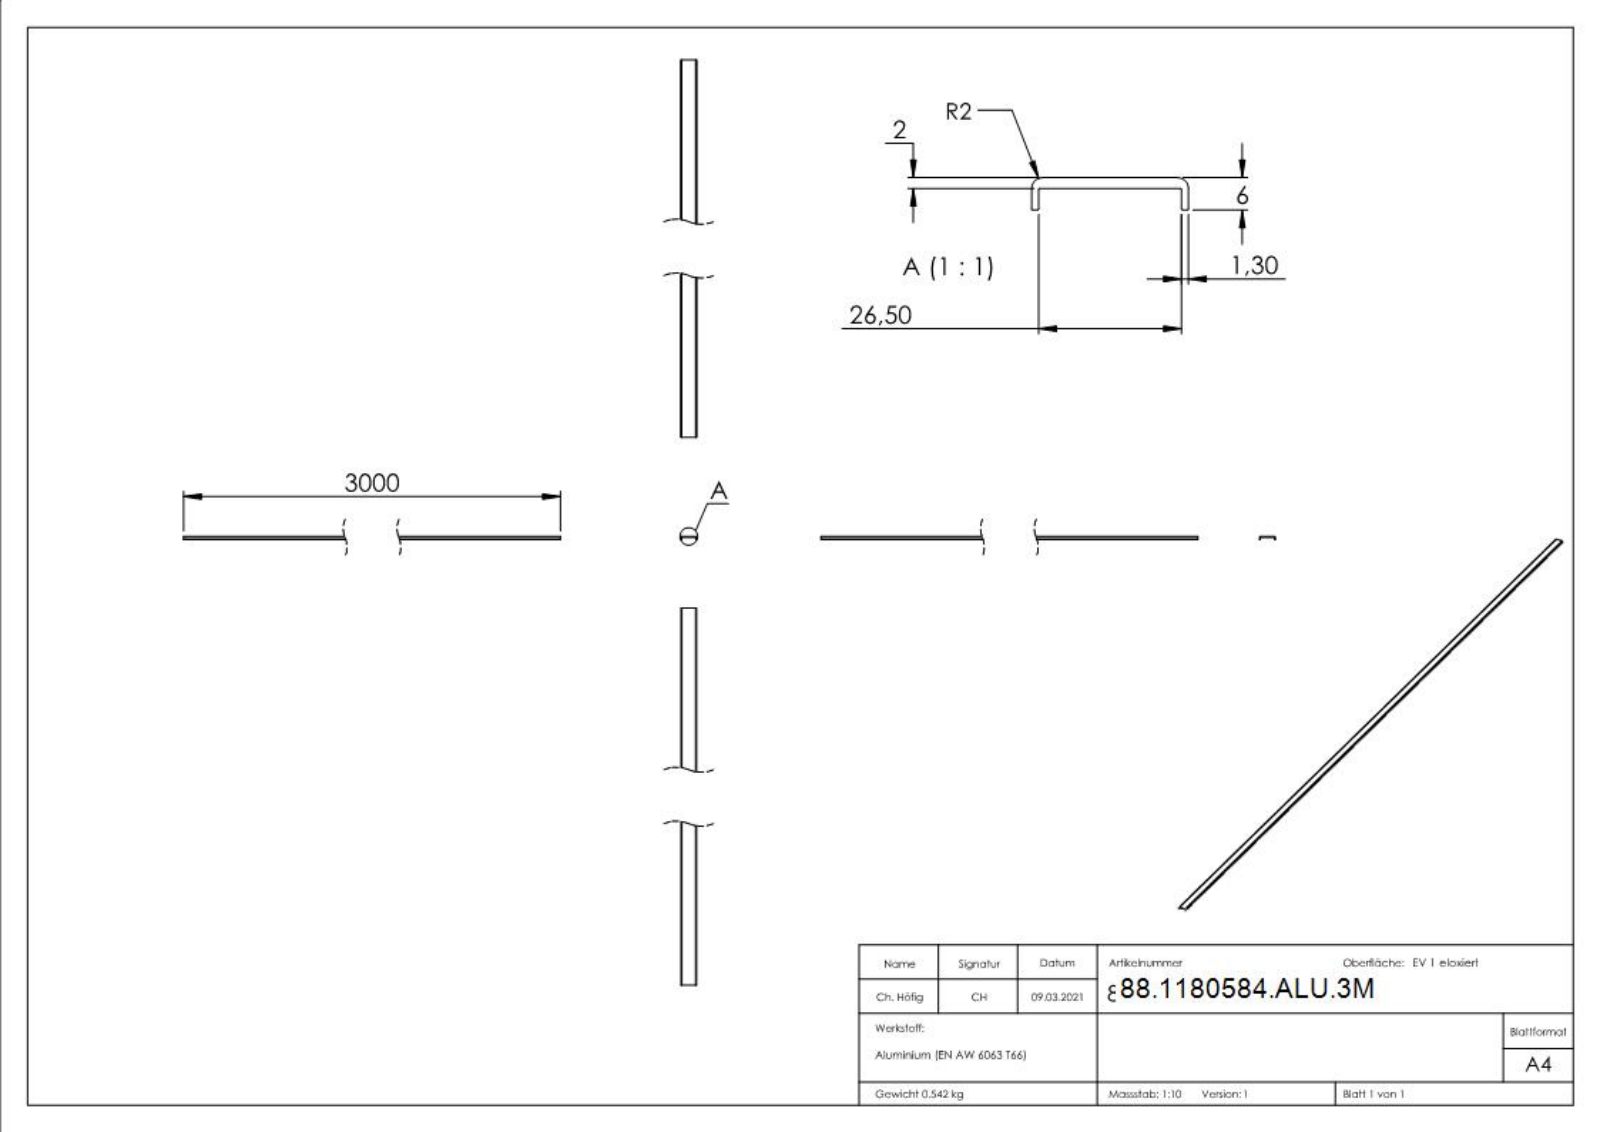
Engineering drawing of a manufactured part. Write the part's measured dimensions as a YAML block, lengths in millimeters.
part_name: "80584-ALU-3M"
step_written_by: "SolidWorks 2018 (CONFIG_CONTROL_DESIGN)"
units: millimeters
bodies: {solids: 1, faces: 342, planar: 195, cylindrical: 8, other: 139}
overall_size: [3000, 29.1, 6]
volume: 200598
surface_area: 228048
partial_cylinders:
  - {radius: 0.2, count: 6}
  - {radius: 2, count: 2}
face_to_face_distances: [2, 1.3, 27.8, 29.1, 26.5, 6, 4, 3000, 4.1, 1.9]
